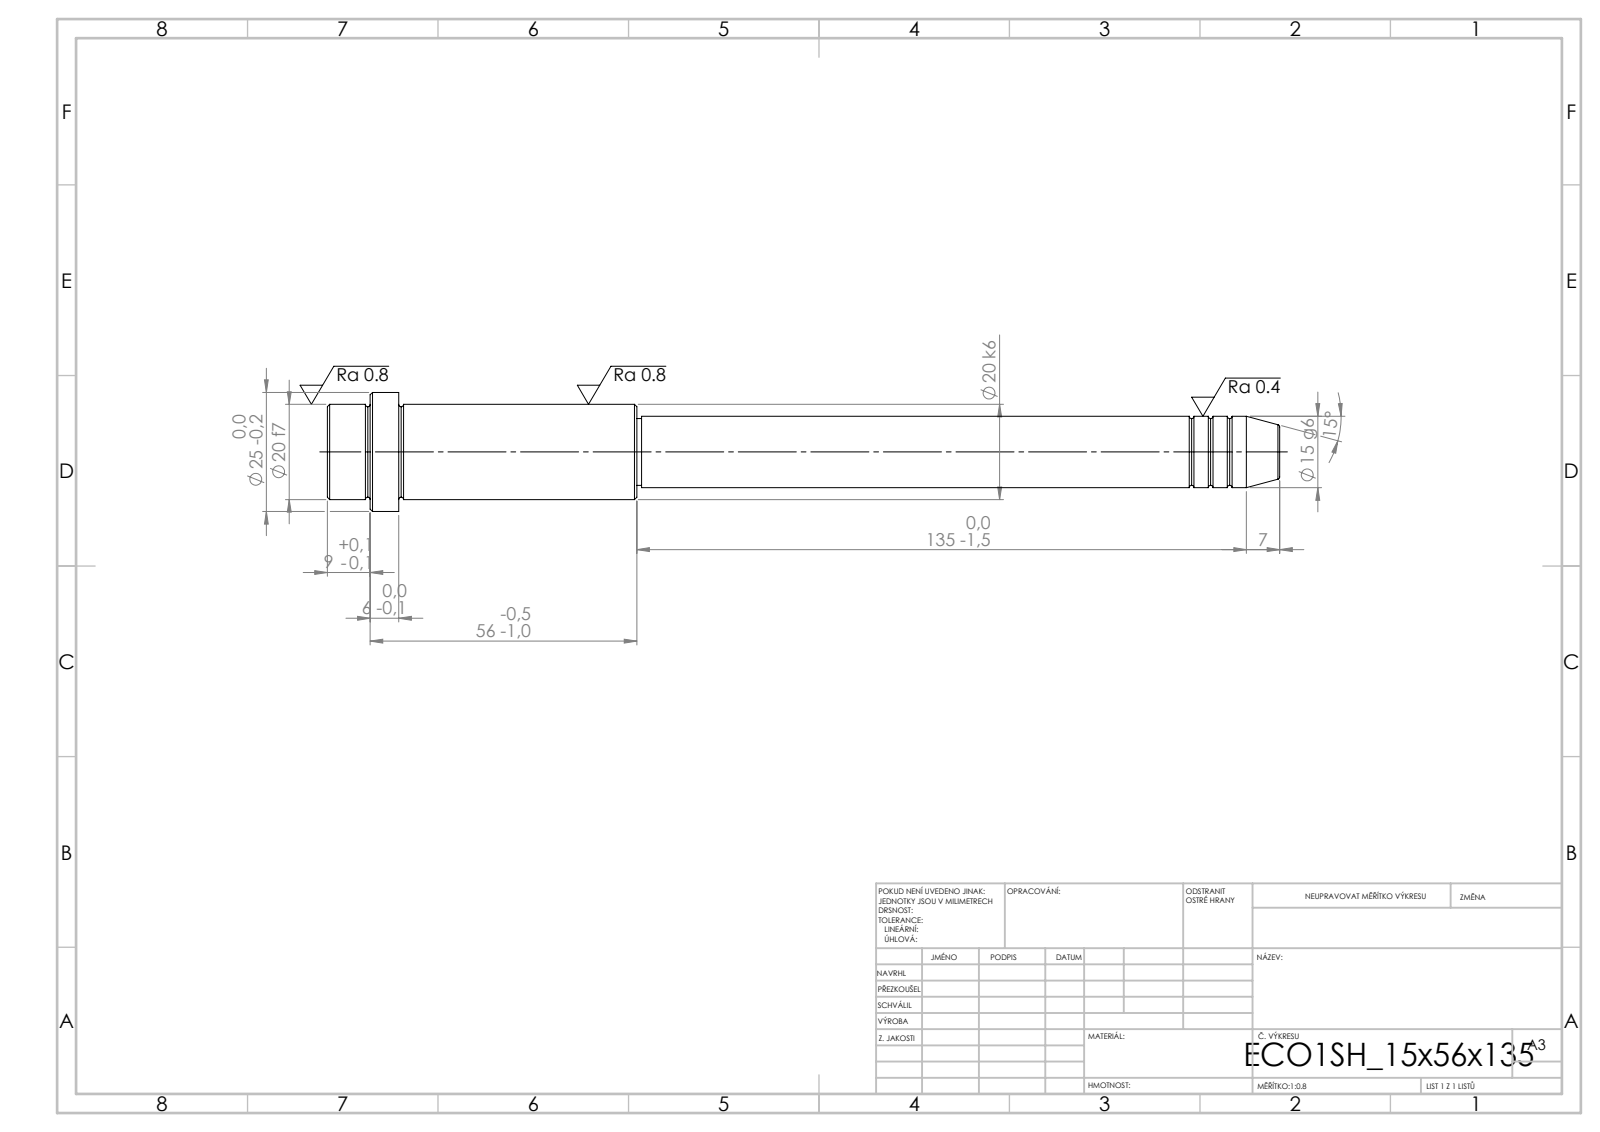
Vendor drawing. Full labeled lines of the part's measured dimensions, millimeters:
STEP written by: SolidWorks 2019 (CONFIG_CONTROL_DESIGN)
Units: millimetres
Bodies: 1 solid, 52 faces (6 planar, 16 cylindrical, 30 other)
Overall size (bounding box): 200 × 25 × 25
Volume: 44 902 mm³ · Surface area: 11 528 mm²
Round bosses / shafts (diameter × count): ⌀25 ×1, ⌀20 ×1, ⌀15 ×1, ⌀14 ×1
Main face-to-face distances: 15, 6, 9, 50, 56, 65, 135, 185, 191, 200
